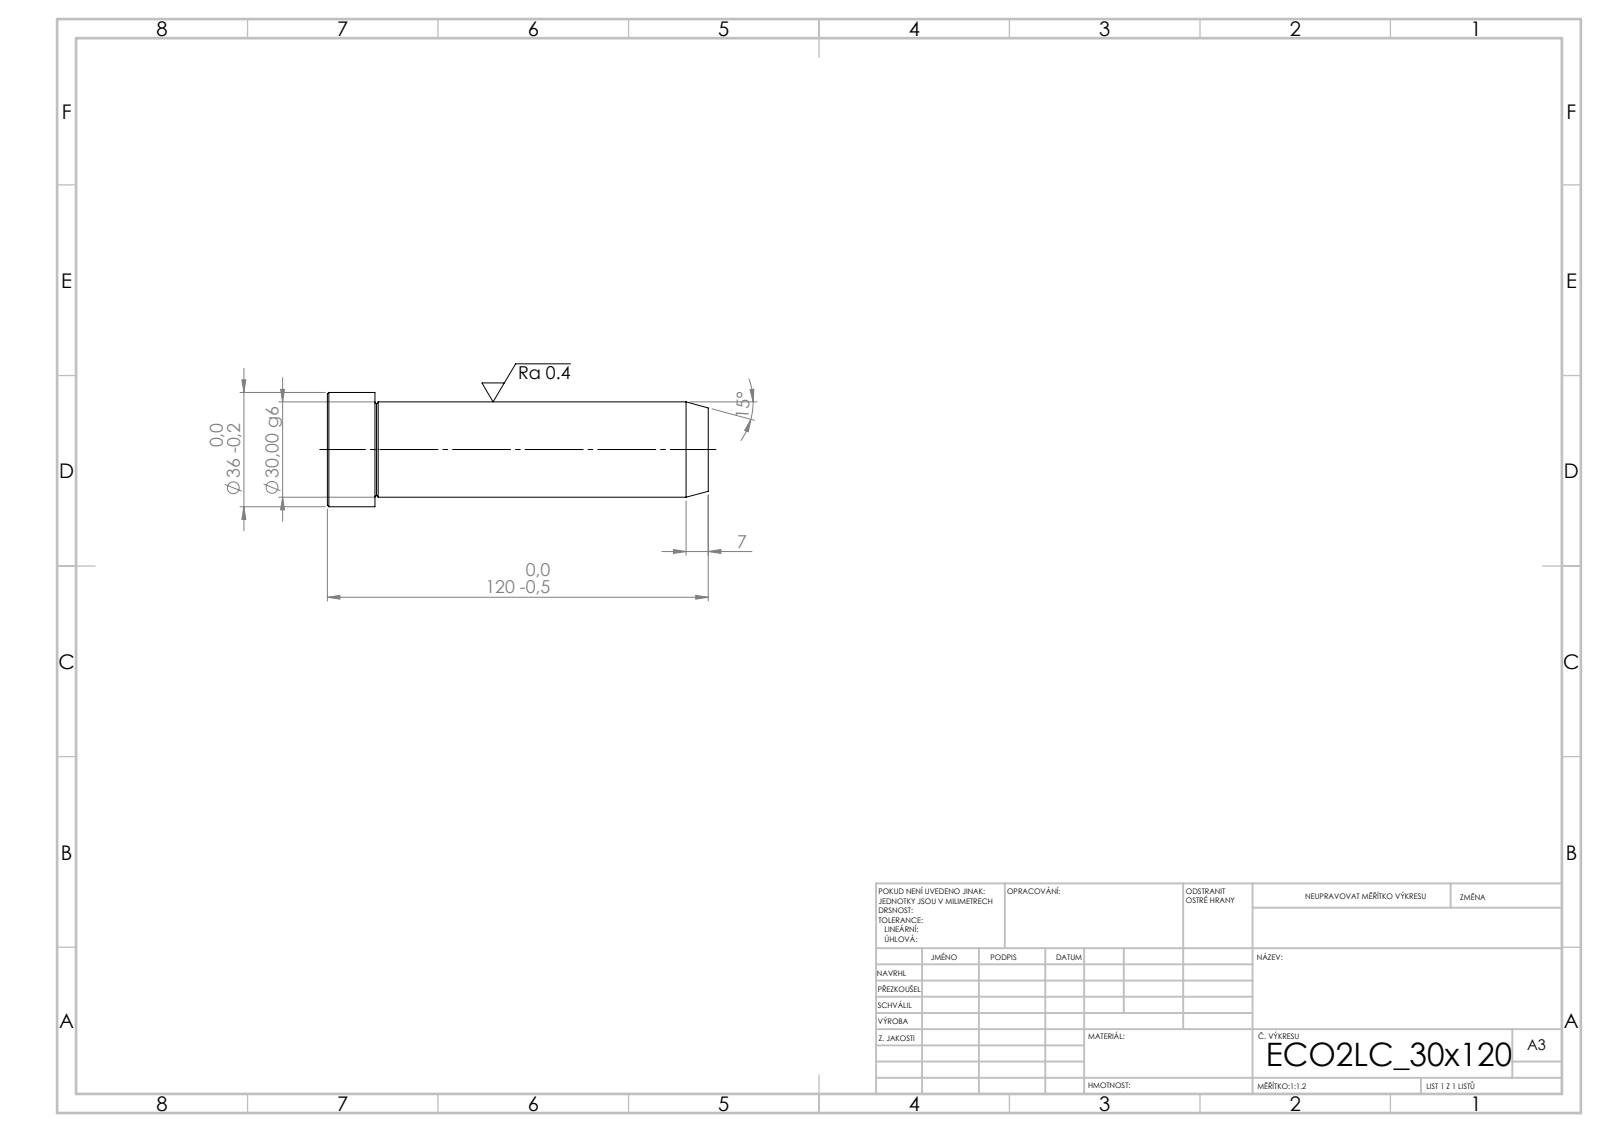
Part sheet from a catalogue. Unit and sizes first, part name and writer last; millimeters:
Units: millimetres
Overall size (bounding box): 120 × 36 × 36
Round bosses / shafts (diameter × count): ⌀36 ×1, ⌀30 ×1
Main face-to-face distances: 120, 105, 15
Volume: 88 845 mm³ · Surface area: 13 460 mm²
Bodies: 1 solid, 15 faces (3 planar, 4 cylindrical, 8 other)
STEP written by: SolidWorks 2019 (CONFIG_CONTROL_DESIGN)
